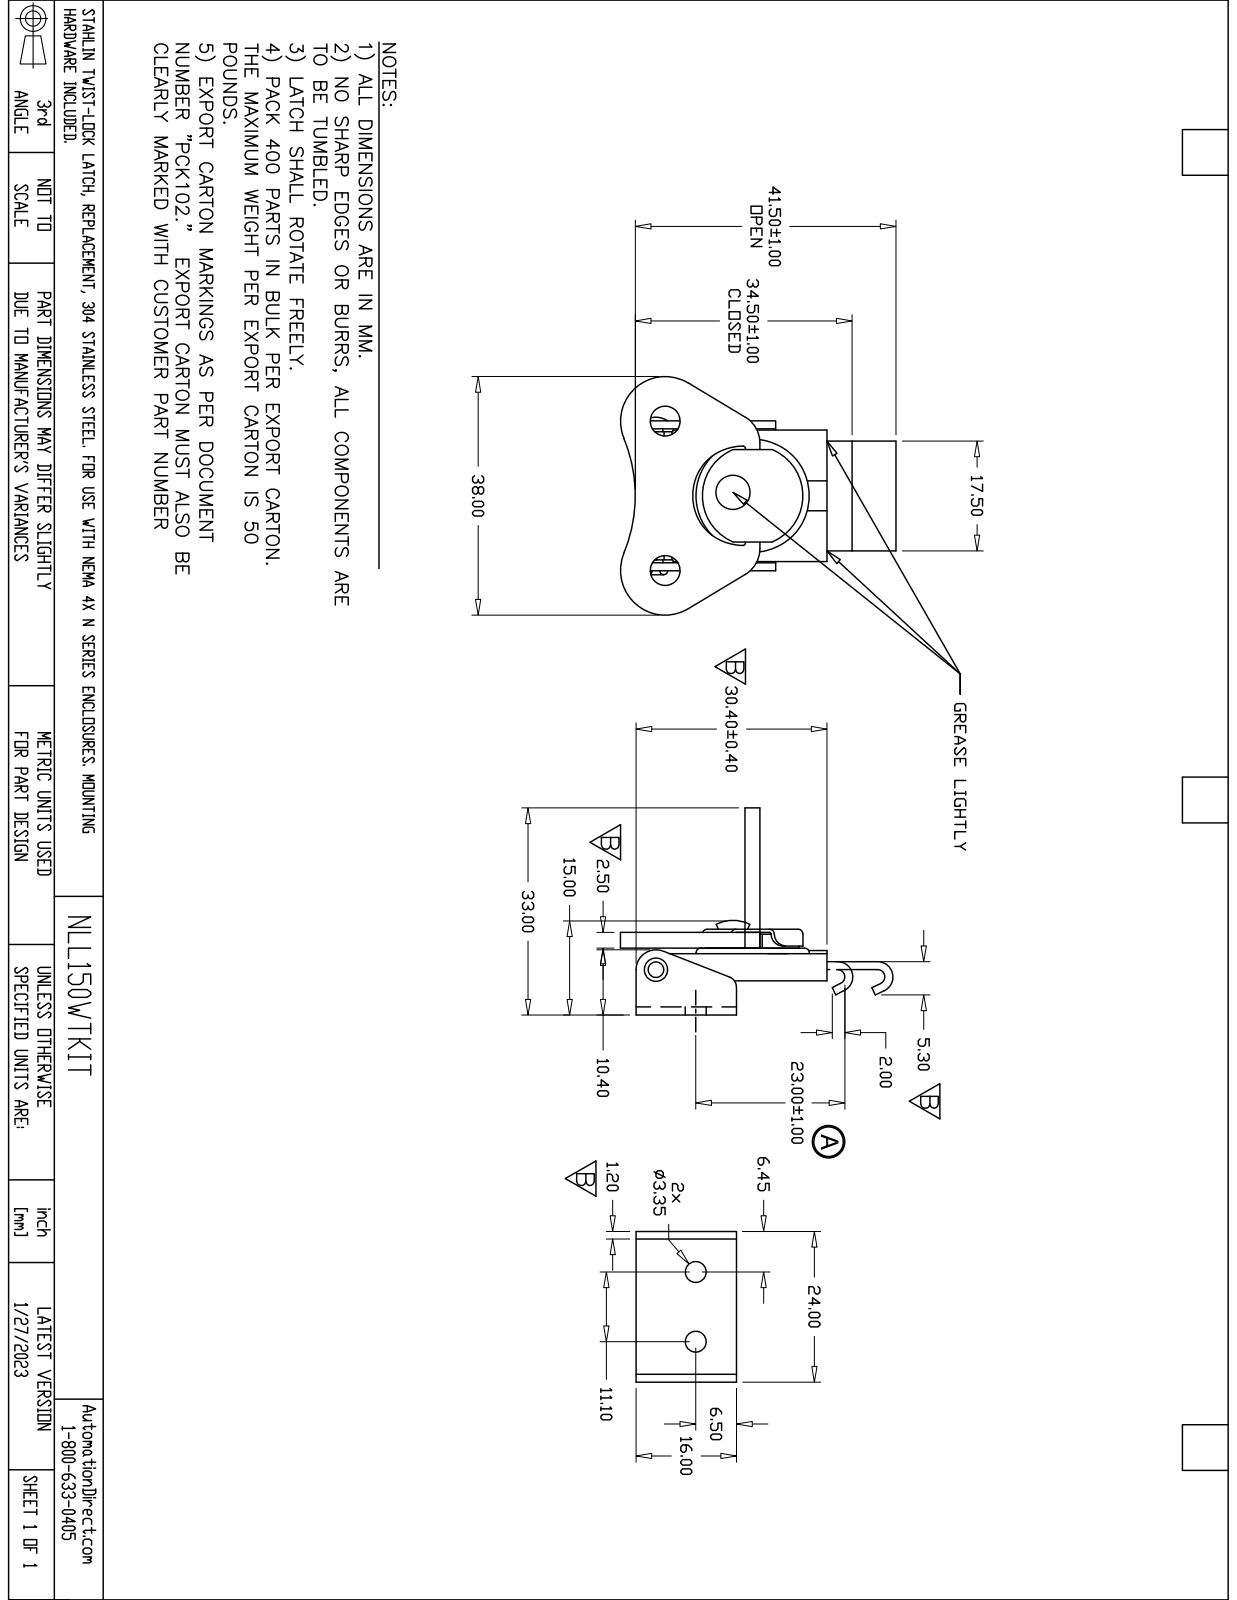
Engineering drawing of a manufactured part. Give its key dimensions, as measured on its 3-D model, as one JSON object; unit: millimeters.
{"part_name": "TLL150WTKIT", "step_written_by": "SolidWorks 2018 (AUTOMOTIVE_DESIGN)", "units": "millimeters", "bodies": {"solids": 16, "faces": 222, "planar": 110, "cylindrical": 99, "other": 13}, "overall_size": [55.7, 42.9, 30.1], "volume_mm3": 5800, "surface_area_mm2": 10230, "round_holes": [[1.9, 2], [2.6, 2], [3.3, 2], [3.4, 2], [3.5, 2], [4.7, 2], [1.7, 1], [2.5, 1], [3.4, 1], [3.6, 1], [4.8, 1], [4.9, 1]], "round_bosses_or_shafts": [[7.2, 2], [3.6, 2], [3.2, 2], [16.8, 1], [14.8, 1], [13.3, 1], [7.3, 1], [5.4, 1]], "partial_cylinders_radius": [[0.4, 8], [0.3, 4], [0.5, 4], [1.5, 4], [1.8, 4], [2, 4], [3.2, 4], [0.8, 3]], "face_to_face_distances": [1.3, 2.1, 1.3, 2.4, 4.4, 5.7, 3.4, 3.2, 0.8, 2.5], "hole_center_spacings": [3.2, 4, 7.1, 12.7, 15.8, 16.5, 18.3, 18.4]}
